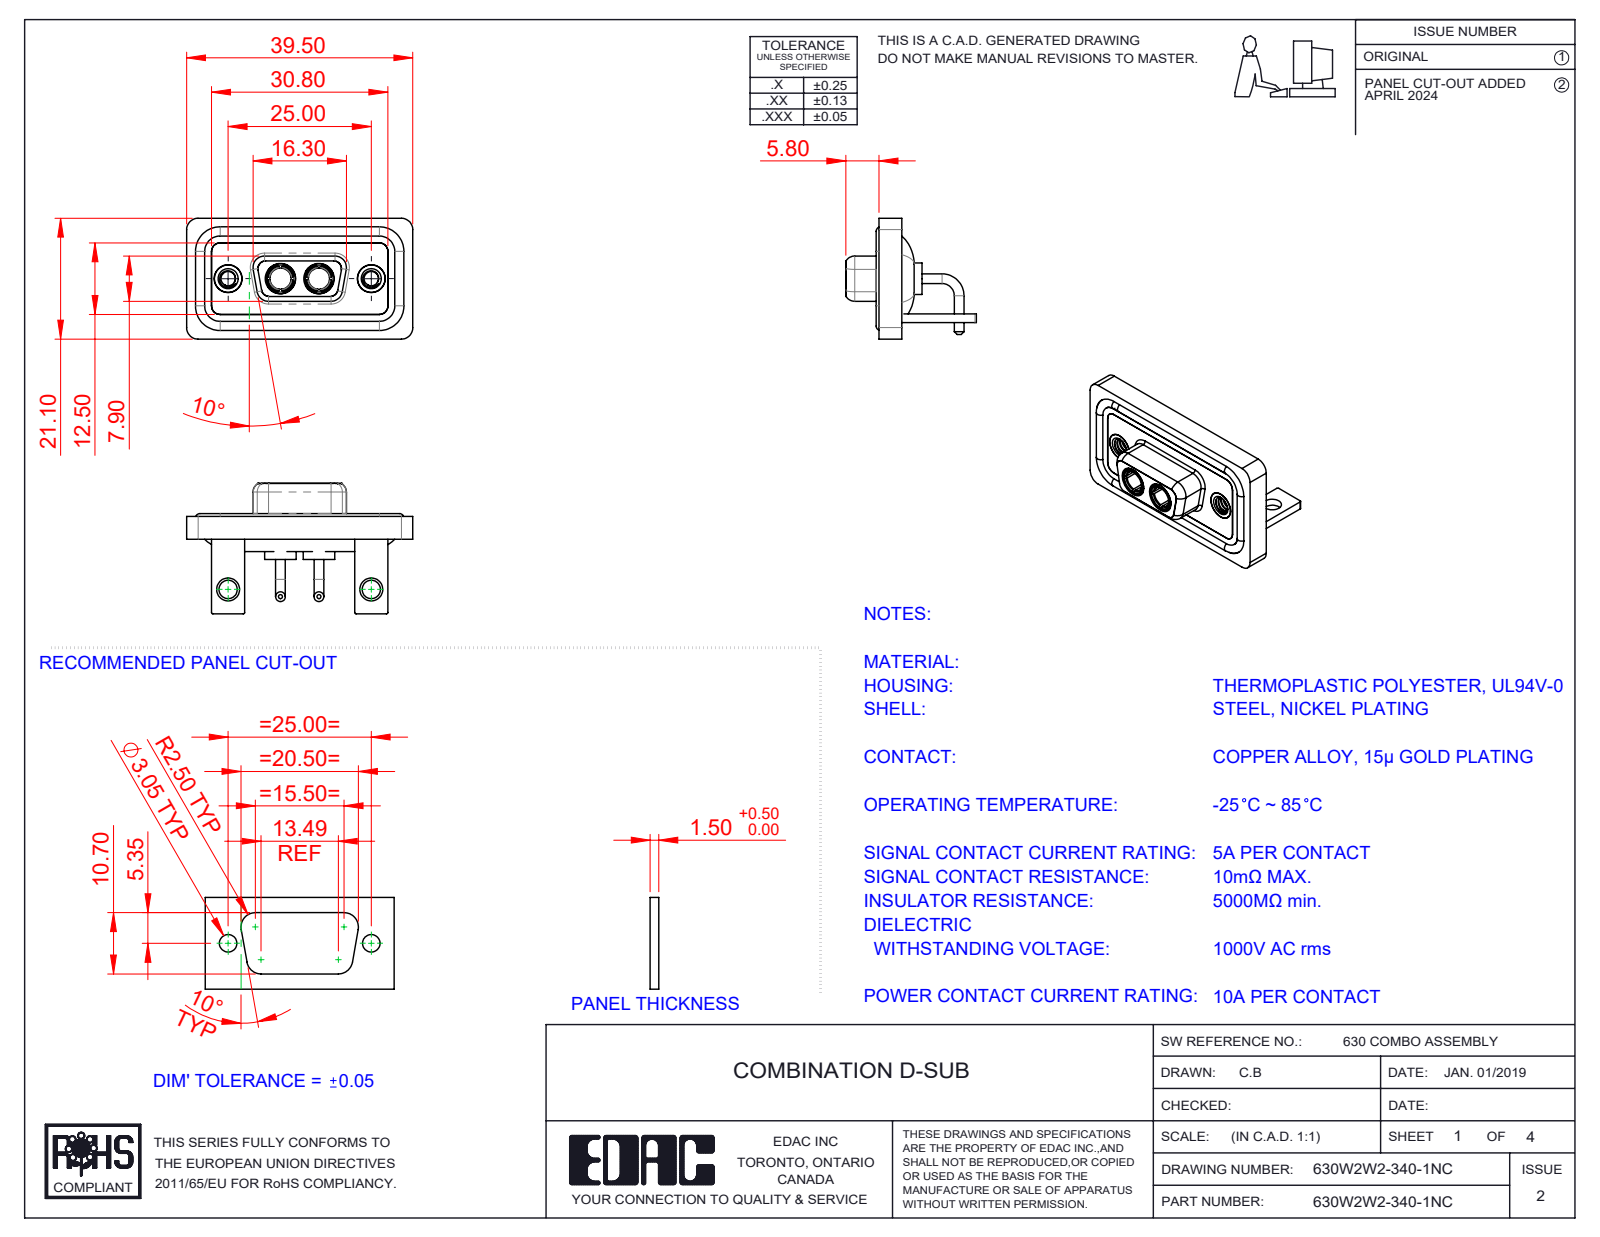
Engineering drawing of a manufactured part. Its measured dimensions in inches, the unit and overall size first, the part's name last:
Units: inches
Overall size (bounding box): 1.555 × 0.898 × 0.831
Round holes (diameter × count): ⌀0.191 ×4, ⌀0.098 ×2, ⌀0.126 ×2, ⌀0.146 ×2, ⌀0.157 ×2, ⌀0.159 ×2, ⌀0.197 ×2, ⌀0.209 ×2
Round bosses / shafts (diameter × count): ⌀0.067 ×4, ⌀0.063 ×4, ⌀0.217 ×2, ⌀0.205 ×2, ⌀0.195 ×2, ⌀0.195 ×2, ⌀0.189 ×2, ⌀0.187 ×2
Partial cylindrical surfaces — rounded edges, fillets, slot ends (radius × count): R0.079 ×19, R0.059 ×18, R0.01 ×16, R0.053 ×8, R0.063 ×8, R0.02 ×5, R0.024 ×4, R0.026 ×4
Main face-to-face distances: 0.016, 0.114, 0.059, 0.071, 0.043, 0.146, 0.031, 0.098, 0.063, 0.122
Hole centre spacings: 0.36, 0.624, 0.984, 0.265
Volume: 0.309 in³ · Surface area: 13.06 in²
Bodies: 13 solids, 584 faces (183 planar, 260 cylindrical, 141 other)
Part name (STEP PRODUCT): 630Combo Shell Front_09 Contacts; 630Combo Stabilizer Bracket_50 Contacts; Power Socket_10A RA; 630Combo Housing_2W2 (+4 more)
STEP written by: SolidWorks 2023 (CONFIG_CONTROL_DESIGN)
